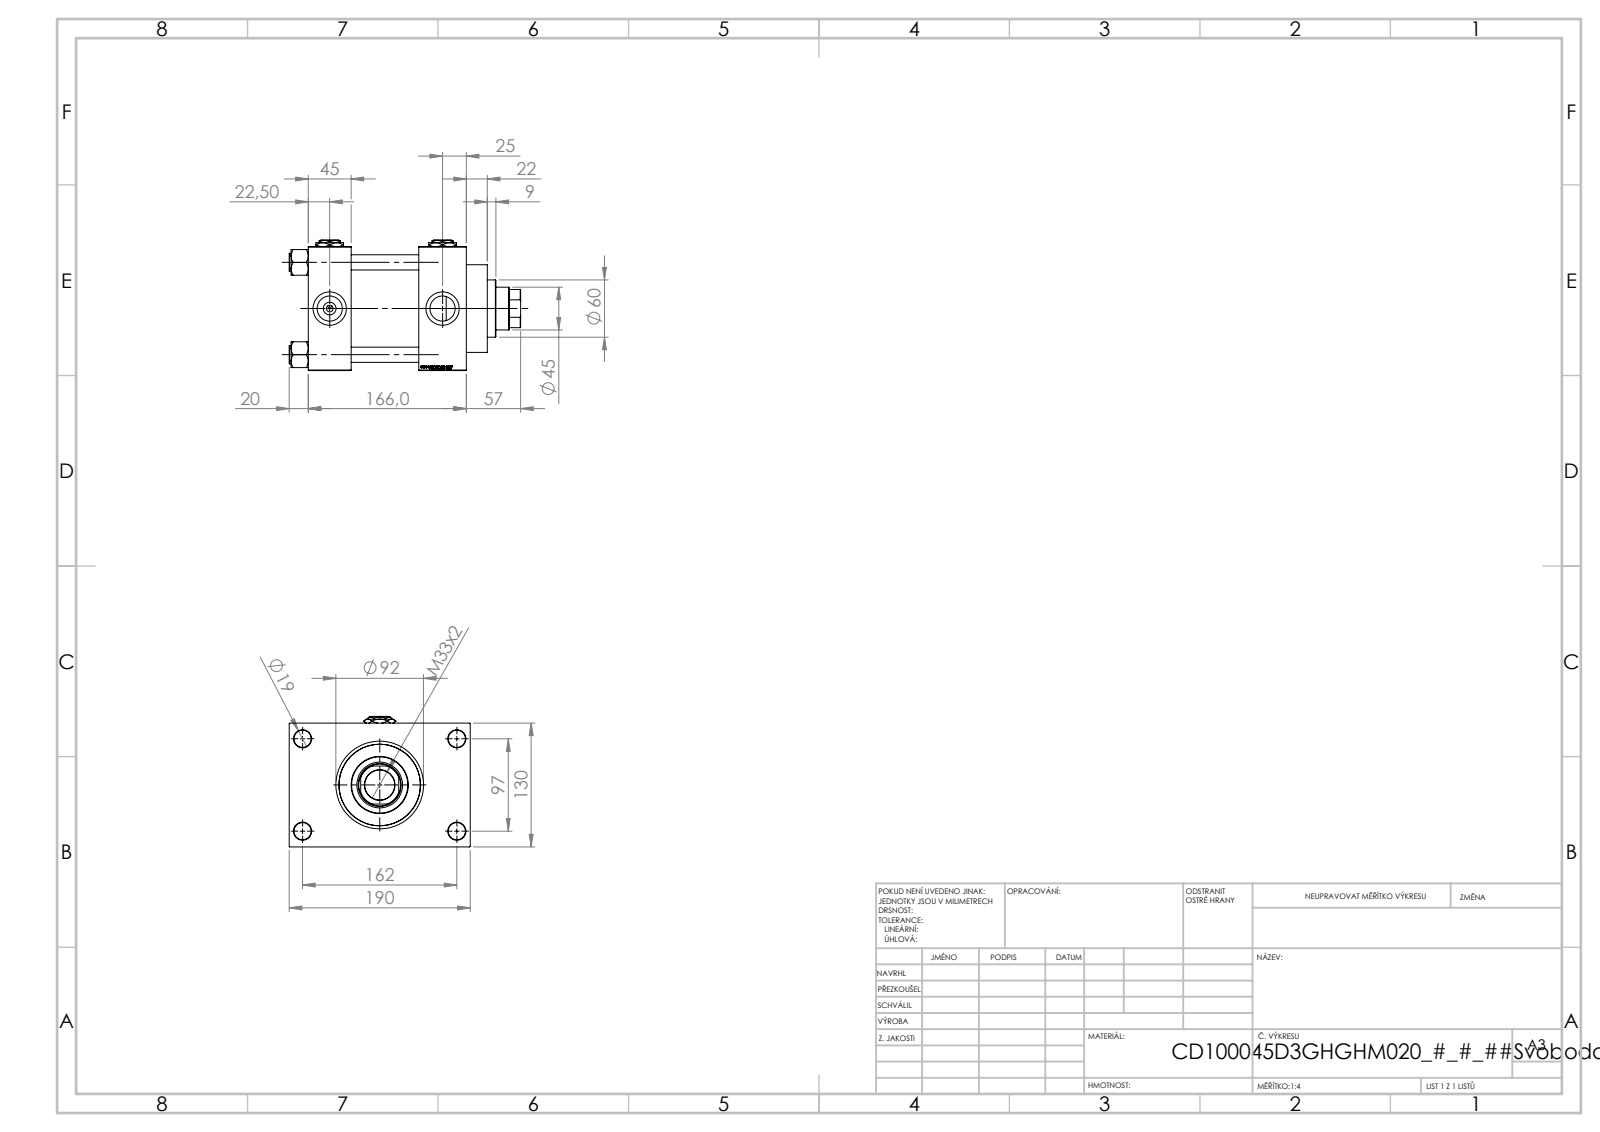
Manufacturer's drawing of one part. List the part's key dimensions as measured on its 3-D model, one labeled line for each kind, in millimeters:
Part name (STEP PRODUCT): V215CD_NUT_M5_D; V215CD_VCP_D; V215CD_D_Body; V215CD_VC_A (+2 more)
STEP written by: SolidWorks 2019 (CONFIG_CONTROL_DESIGN)
Units: millimetres
Bodies: 13 solids, 1252 faces (593 planar, 99 cylindrical, 560 other)
Overall size (bounding box): 243 × 190 × 137
Volume: 2 576 000 mm³ · Surface area: 361 795 mm²
Round holes (diameter × count): ⌀16 ×4, ⌀18 ×4, ⌀26.44 ×4, ⌀35 ×4, ⌀7 ×3, ⌀31.5 ×1, ⌀45 ×1, ⌀48 ×1, ⌀76 ×1, ⌀85.5 ×1, ⌀100 ×1
Round bosses / shafts (diameter × count): ⌀19 ×4, ⌀106 ×1, ⌀92 ×1, ⌀60 ×1
Partial cylindrical surfaces — rounded edges, fillets, slot ends (radius × count): R22 ×1
Main face-to-face distances: 45, 130, 116, 71, 166, 121, 50, 30, 160, 20
Hole centre spacings: 32.55, 68.52, 94.41, 96.9, 102.27, 129.45, 161.73, 97
